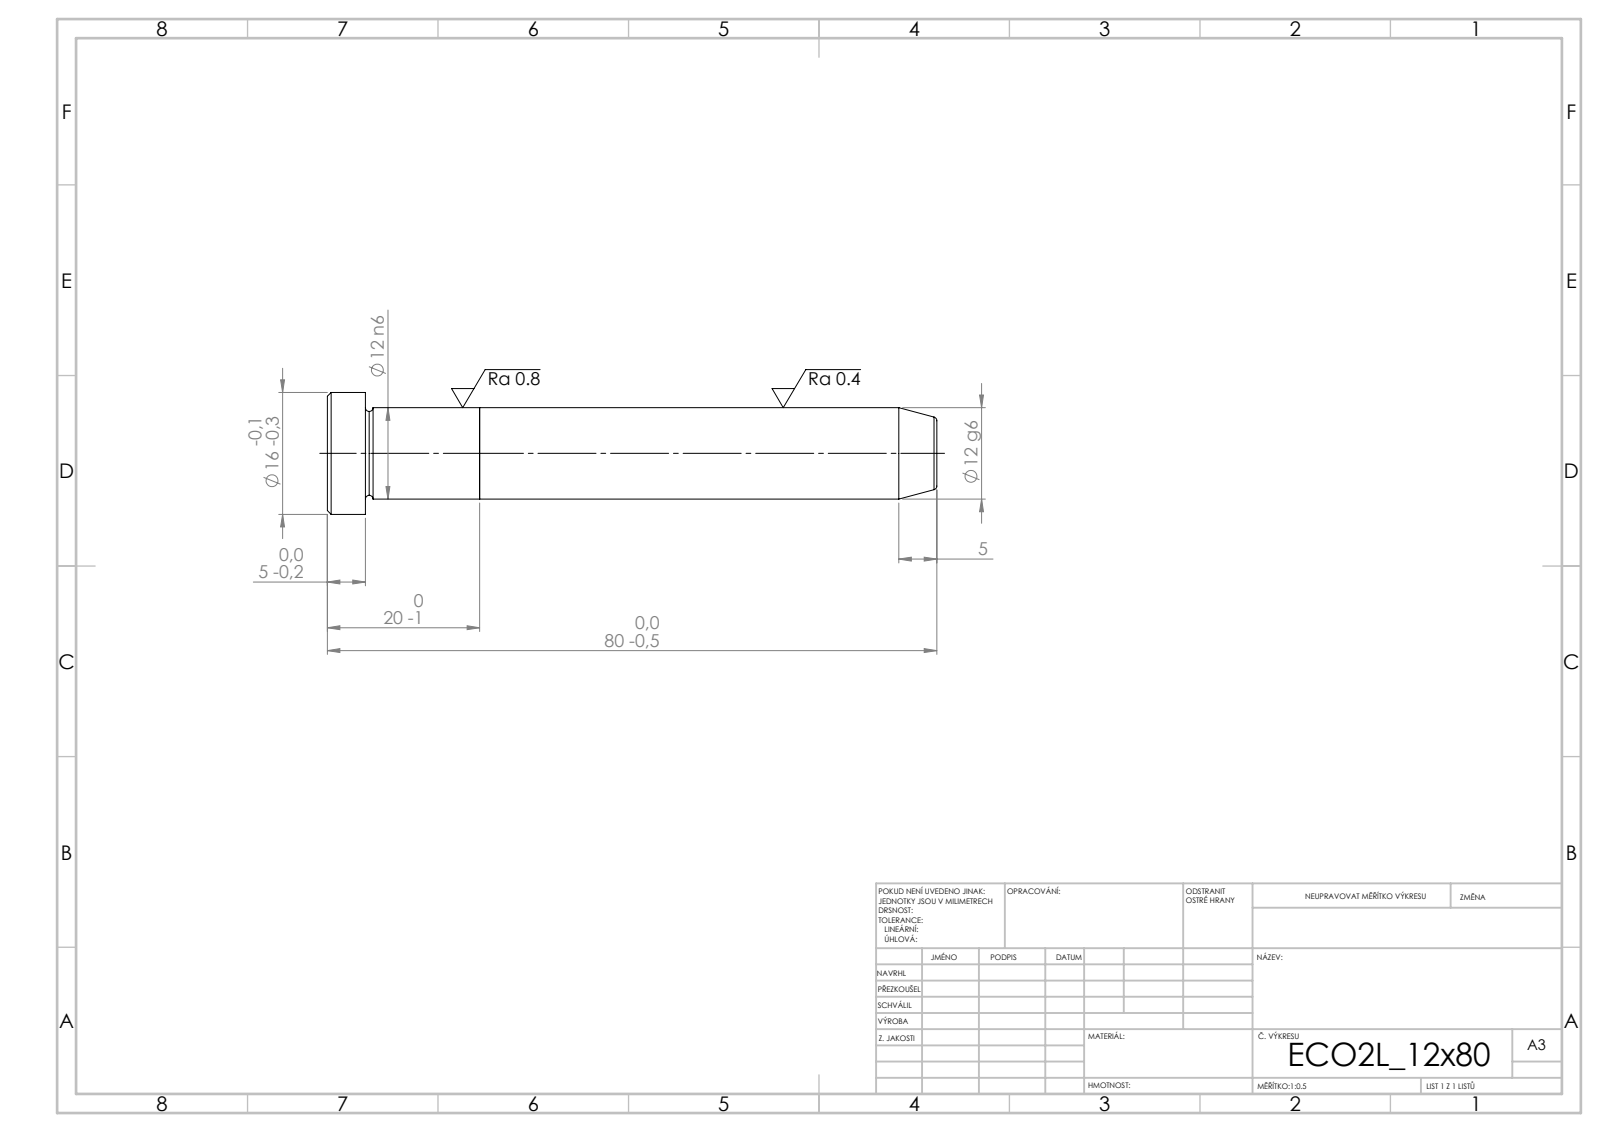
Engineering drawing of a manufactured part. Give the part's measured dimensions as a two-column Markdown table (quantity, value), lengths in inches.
| quantity | value |
| --- | --- |
| STEP written by | SolidWorks 2019 (CONFIG_CONTROL_DESIGN) |
| units | inches |
| bodies | 2 solids, 21 faces (5 planar, 6 cylindrical, 10 other) |
| overall size | 3.15 × 0.63 × 0.63 |
| volume | 0.571 in³ |
| surface area | 5.653 in² |
| round bosses / shafts (diameter × count) | 0.63 × 1, 0.472 × 1 |
| main face-to-face distances | 0.787, 0.591, 0.197, 2.362, 2.953, 3.15 |
